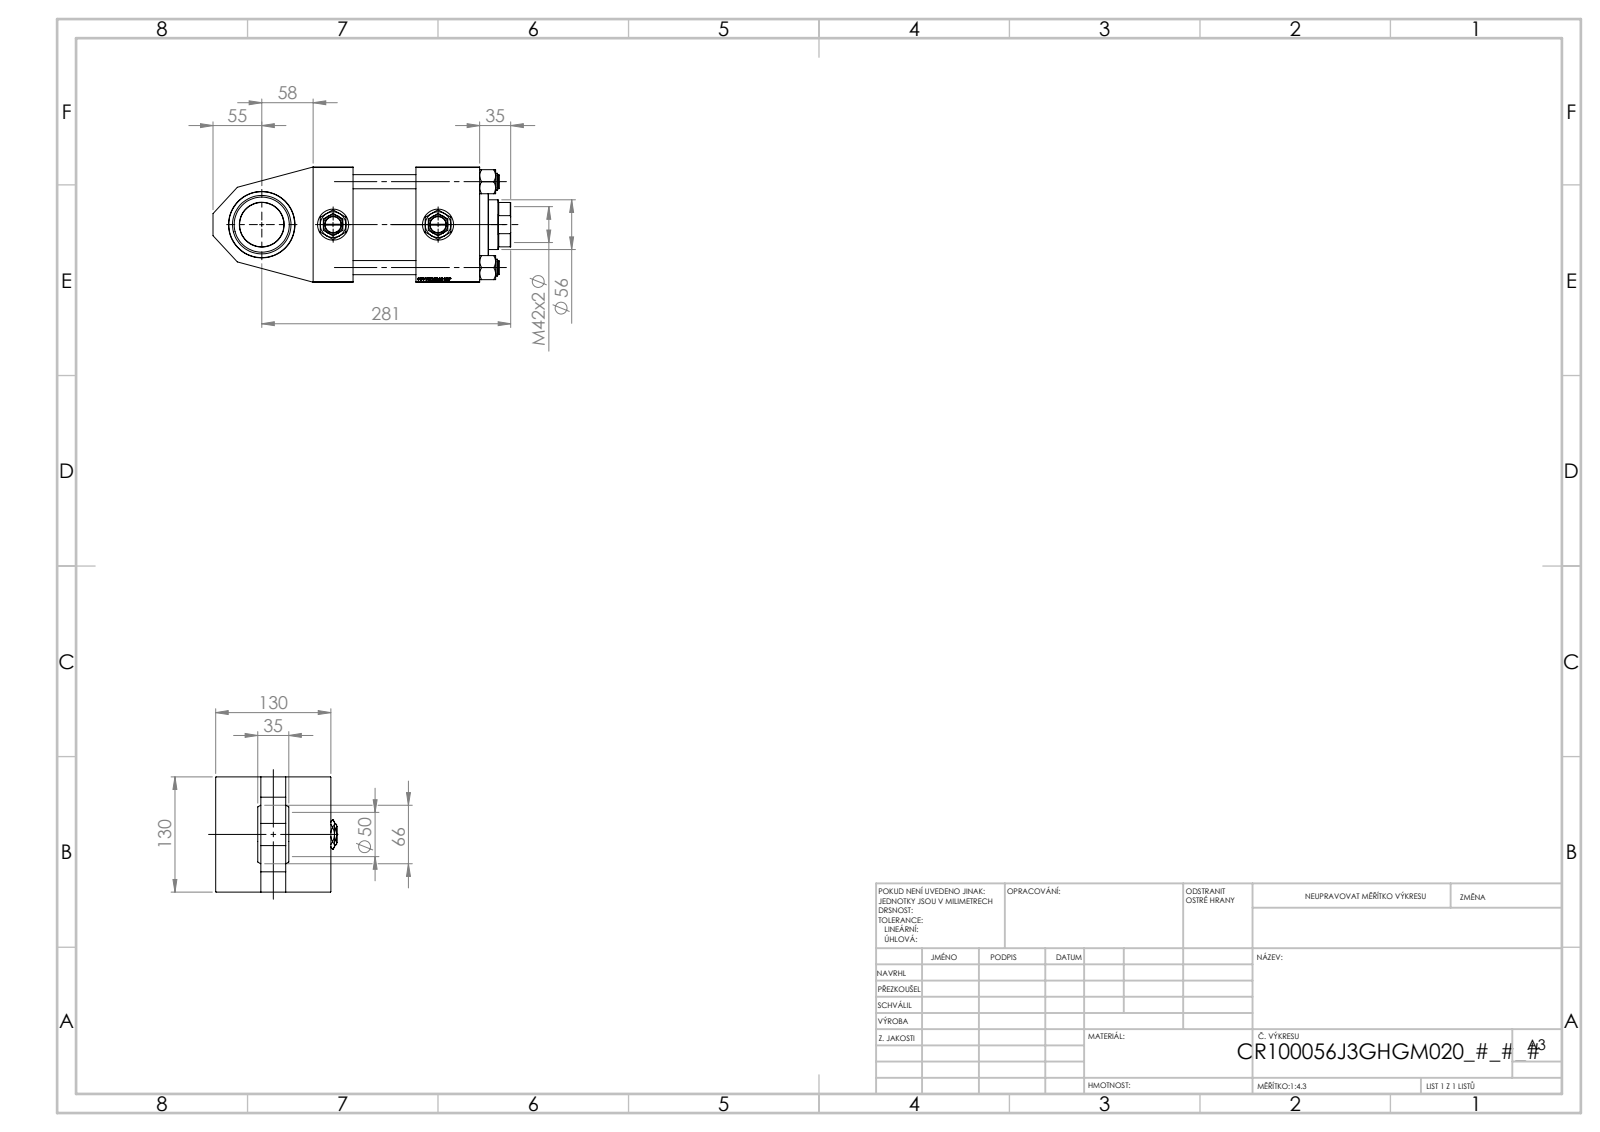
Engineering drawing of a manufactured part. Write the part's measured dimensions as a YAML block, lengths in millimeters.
part_name: "V215CR_J_Body; V215CR_J_VNITRNI_KROUZEK; V215_VC_A; Zatka_pro_OIL_PORT (+3 more)"
step_written_by: "SolidWorks 2019 (CONFIG_CONTROL_DESIGN)"
units: millimeters
bodies: {solids: 14, faces: 1294, planar: 612, cylindrical: 100, other: 582}
overall_size: [336, 137, 130]
volume: 2737000
surface_area: 386389
round_holes:
  - {diameter: 16, count: 4}
  - {diameter: 2.5, count: 2}
  - {diameter: 7, count: 2}
  - {diameter: 26.44, count: 2}
  - {diameter: 35, count: 2}
  - {diameter: 40.5, count: 1}
  - {diameter: 50, count: 1}
  - {diameter: 56, count: 1}
  - {diameter: 59, count: 1}
  - {diameter: 75, count: 1}
  - {diameter: 76, count: 1}
  - {diameter: 85.5, count: 1}
round_bosses_or_shafts:
  - {diameter: 19, count: 4}
  - {diameter: 106, count: 1}
  - {diameter: 72, count: 1}
partial_cylinders:
  - {radius: 27, count: 1}
face_to_face_distances: [130, 51, 79, 45, 188, 143, 71, 116, 72, 28]
hole_center_spacings: [49.02, 68.52, 96.9, 101.73, 41, 137.04, 80.5, 82]
